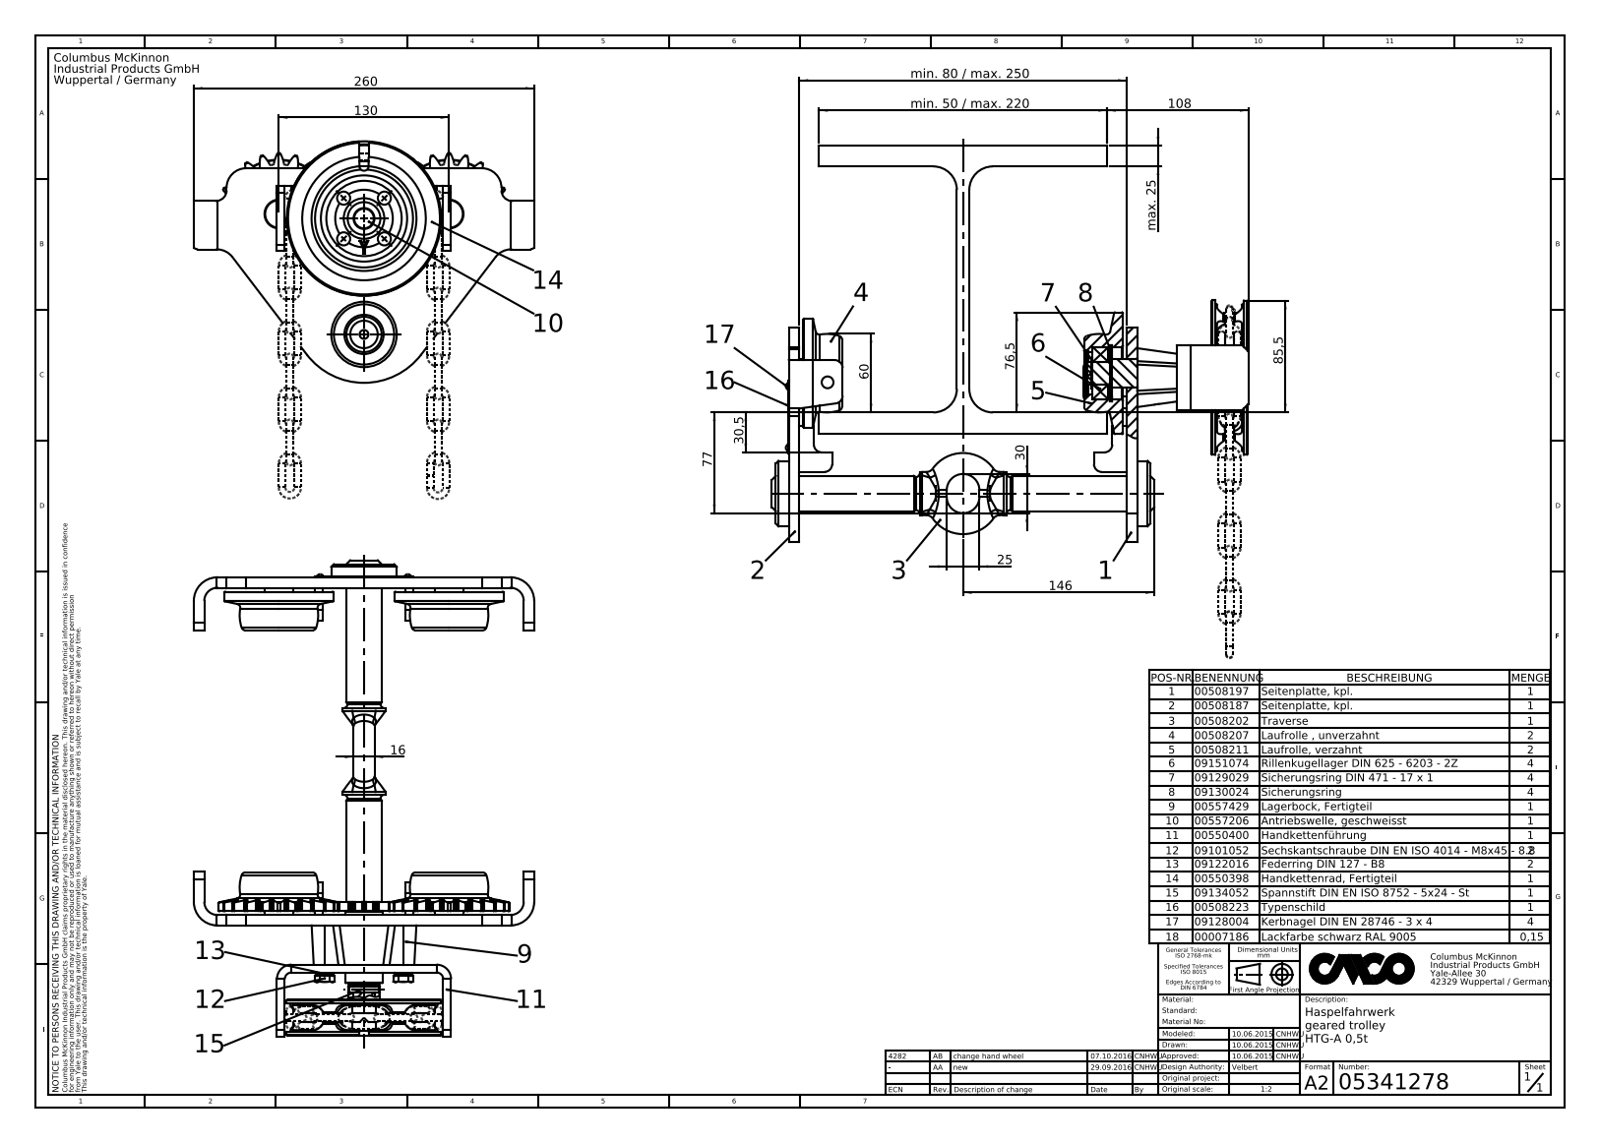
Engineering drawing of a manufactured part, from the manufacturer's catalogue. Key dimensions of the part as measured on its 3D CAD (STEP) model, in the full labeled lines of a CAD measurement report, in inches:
Part name (STEP PRODUCT): 05341278
STEP written by: SolidWorks 2015 (AUTOMOTIVE_DESIGN)
Units: inches
Bodies: 68 solids, 1982 faces (432 planar, 924 cylindrical, 626 other)
Overall size (bounding box): 19.685 × 15.425 × 14.331
Volume: 360 in³ · Surface area: 1 685 in²
Round holes (diameter × count): ⌀0.067 ×8, ⌀0.098 ×8, ⌀0.118 ×5, ⌀0.138 ×4, ⌀0.354 ×4, ⌀0.394 ×4, ⌀0.268 ×3, ⌀0.079 ×2, ⌀0.319 ×2, ⌀0.638 ×2, ⌀0.866 ×2, ⌀1.217 ×2
Round bosses / shafts (diameter × count): ⌀0.197 ×22, ⌀0.205 ×4, ⌀3.268 ×2, ⌀1.673 ×2, ⌀0.937 ×2, ⌀0.669 ×2, ⌀0.63 ×2, ⌀0.555 ×2
Partial cylindrical surfaces — rounded edges, fillets, slot ends (radius × count): R0.039 ×110, R0.787 ×88, R0.059 ×48, R0.394 ×26, R0.067 ×8, R0.098 ×8, R0.236 ×8, R0.709 ×8
Main face-to-face distances: 0.63, 8.031, 8.661, 7.402, 0.374, 5.049, 5.423, 0.315, 10.157, 4.734
Hole centre spacings: 0.393, 5.118, 0.722, 0.836, 0.167, 0.246, 0.33, 1.895
